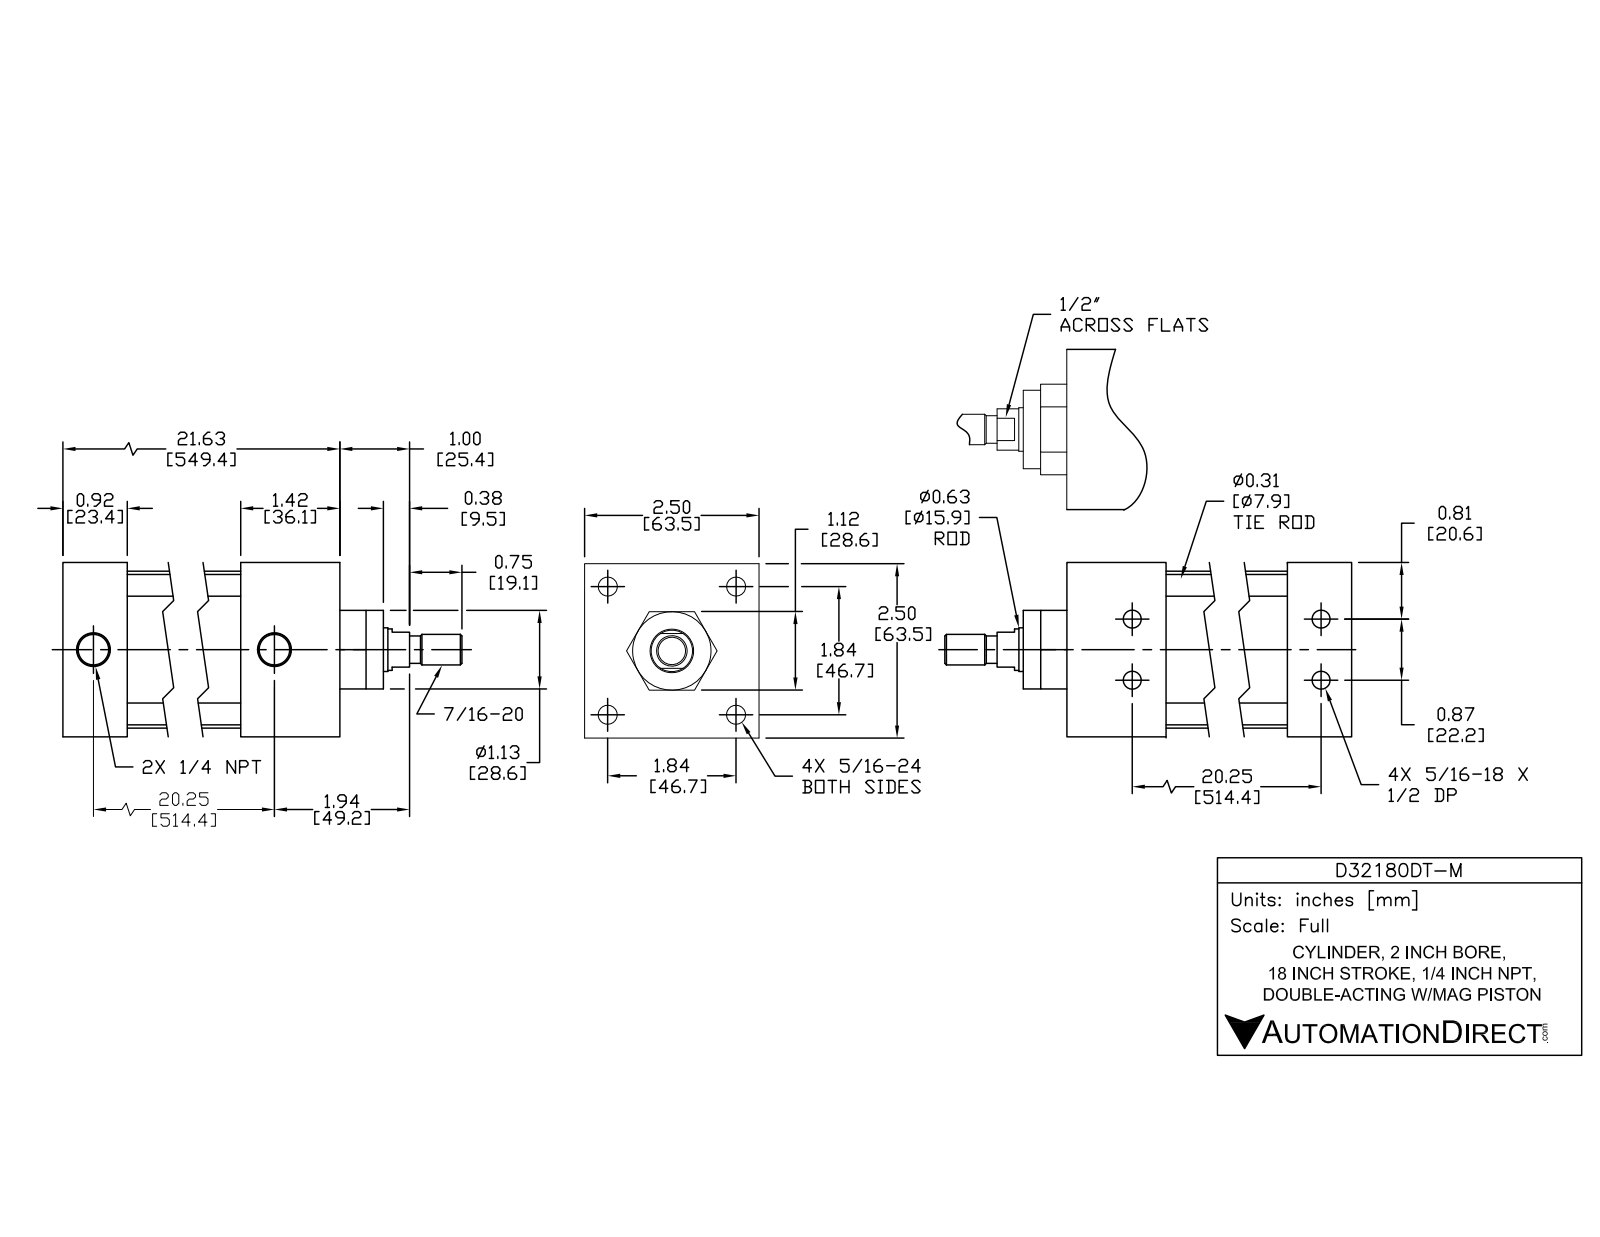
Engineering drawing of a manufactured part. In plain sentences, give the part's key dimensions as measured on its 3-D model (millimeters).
The part is named "D32180DT-M PISTON; D32180DT-M; D32180DT-M BODY". Its 3-D file was written by "SolidWorks 2015 (AUTOMOTIVE_DESIGN)". It is 12 solids with 298 faces: 94 planar, 114 cylindrical and 90 other. Overall it measures 542.8 by 63.5 by 63.5 millimeters. Its volume is 689 100 cubic millimeters and its surface area 274 300 square millimeters. Round holes: 4 of diameter 6.4, 4 of diameter 6.8, 4 of diameter 9.1, 4 of diameter 12.7, 2 of diameter 7.5, 2 of diameter 12.1, 1 of diameter 15.9, 1 of diameter 16, 1 of diameter 50.8. Round bosses or shafts: 4 of diameter 12.3, 4 of diameter 8, 4 of diameter 7.2, 1 of diameter 57.2, 1 of diameter 50.7, 1 of diameter 28.4, 1 of diameter 15.8, 1 of diameter 15. Partial cylindrical surfaces (rounded edges, fillets, slot ends): 4 of radius 6.4. The main face-to-face distances are 63.5, 2, 436.9, 498.4, 36.1, 462.3, 438.9, 475, 23.4, 25.4. The hole center spacings are 11.1, 33.2, 46.9, 463.6, 463.4, 22.2, 66.4, 464.
